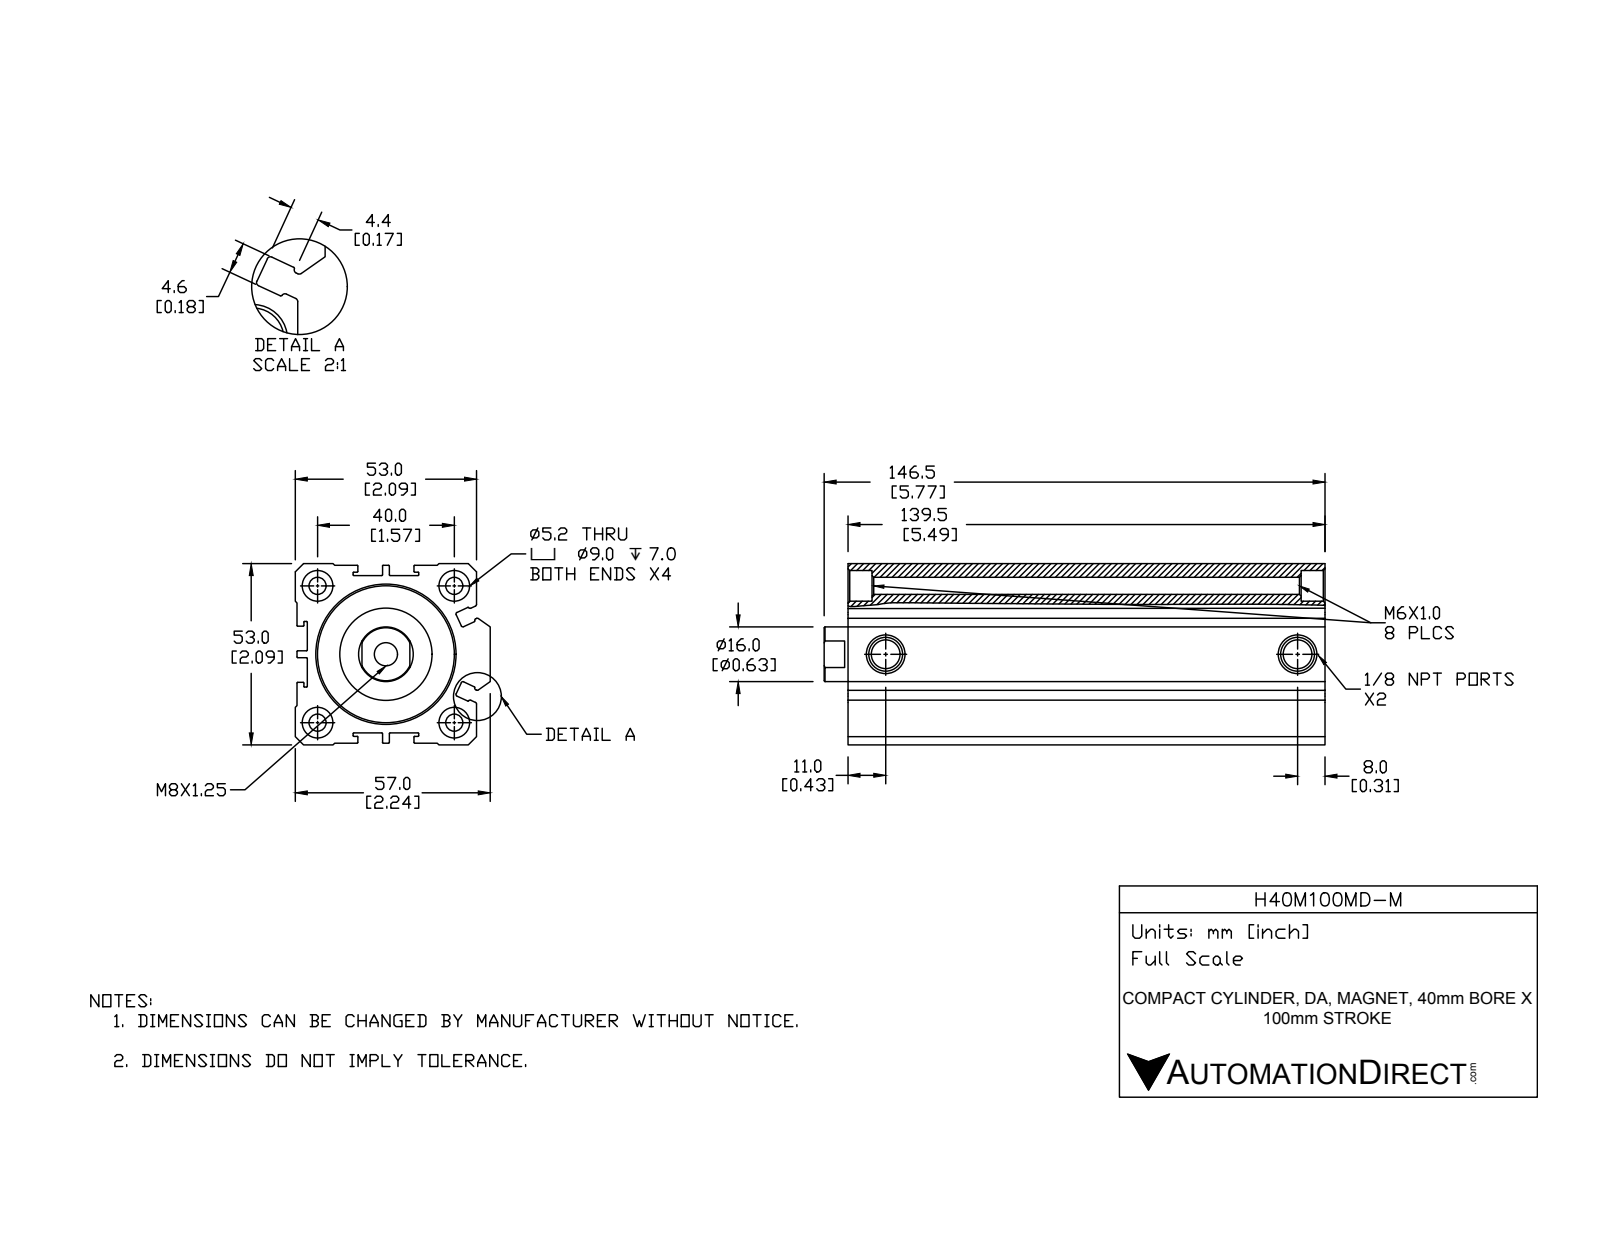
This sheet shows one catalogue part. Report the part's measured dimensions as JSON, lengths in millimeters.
{"part_name": "H40M100MD-M-PISTON; H40M100MD-M-BODY; H40M100MD-M", "step_written_by": "SolidWorks 2015 (CONFIG_CONTROL_DESIGN)", "units": "millimeters", "bodies": {"solids": 2, "faces": 255, "planar": 99, "cylindrical": 103, "other": 53}, "overall_size": [146.5, 57, 53], "volume_mm3": 242033, "surface_area_mm2": 85528, "round_holes": [[5, 4], [9, 4], [8.43, 2], [6.8, 1], [16, 1], [29.5, 1], [40, 1]], "round_bosses_or_shafts": [[27, 1], [25, 1]], "partial_cylinders_radius": [[0.2, 40], [0.5, 12]], "face_to_face_distances": [3.5, 49.5, 0.5, 3, 52.5, 53, 49, 25, 46, 25.5], "hole_center_spacings": [28.28, 40, 56.57, 120.5]}
